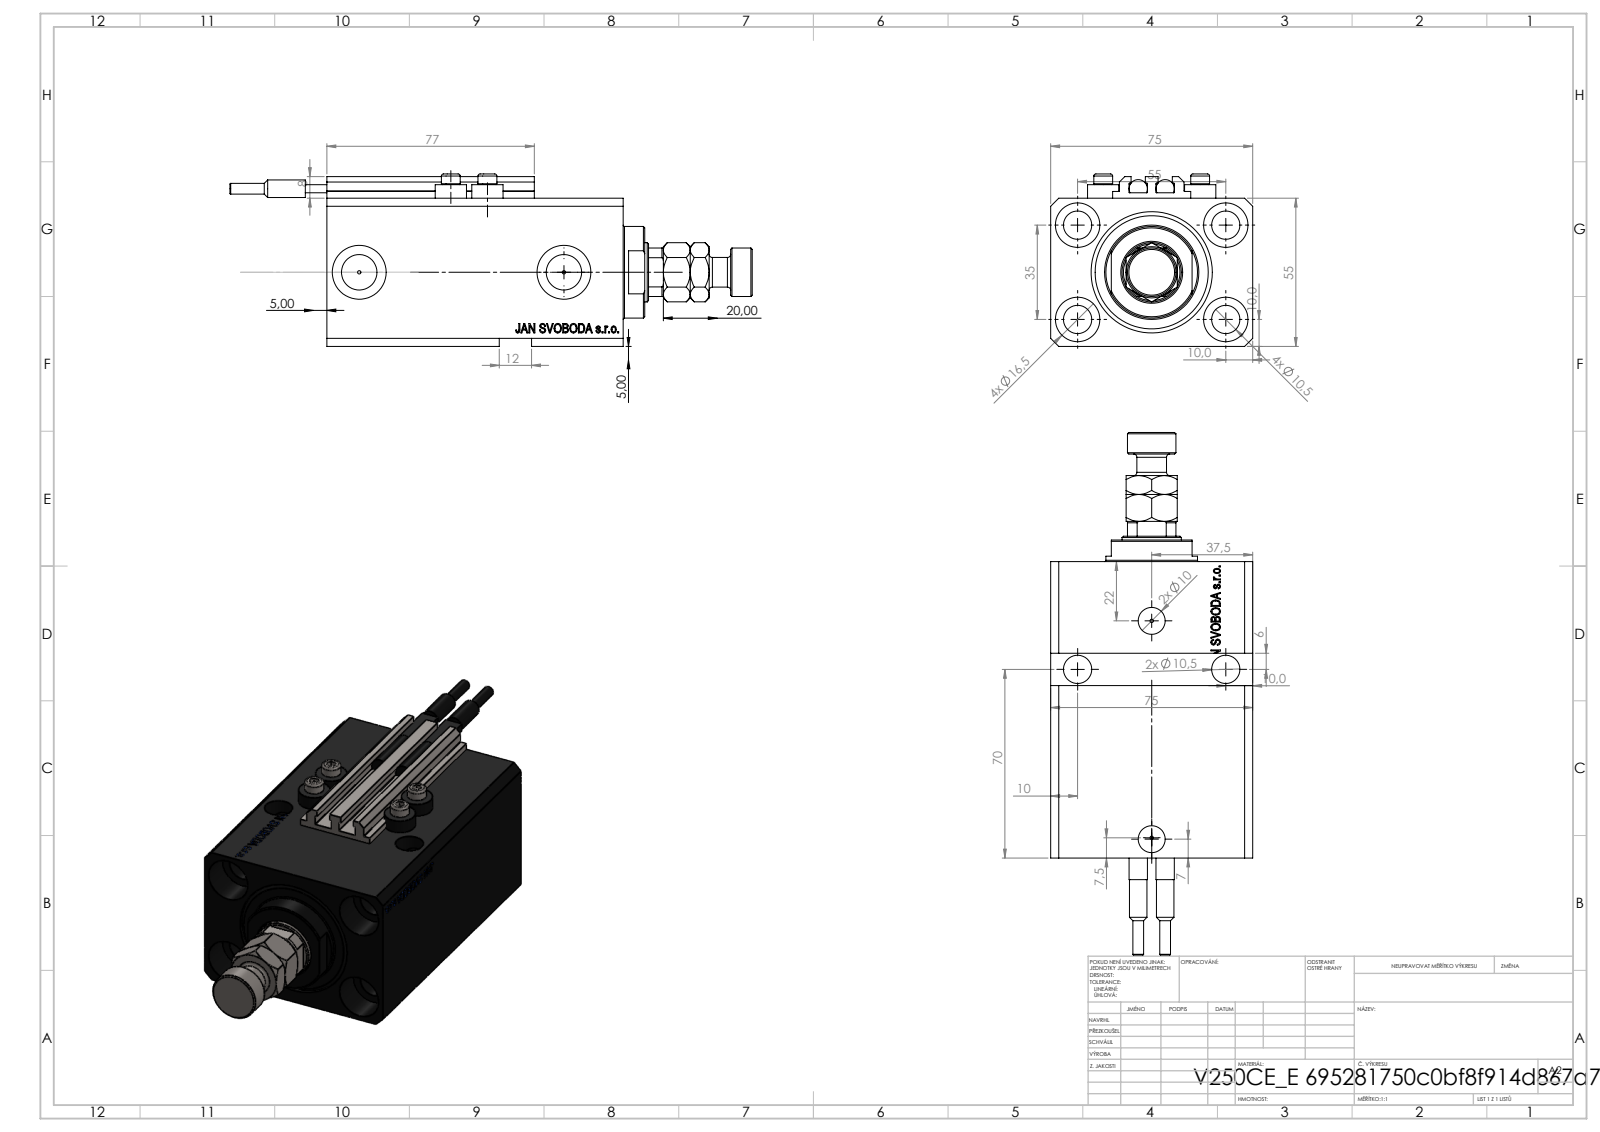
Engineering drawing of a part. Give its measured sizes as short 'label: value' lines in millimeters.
name: V250CE_C_VCP; MFA; V250CE_VC_E; V250CE_E_Body (+2 more)
written by: SolidWorks 2019 (CONFIG_CONTROL_DESIGN)
unit: mm
bodies: 11 solids, 1188 faces (562 planar, 162 cylindrical, 464 other)
size: 194 × 75 × 64
volume: 392 978 mm³; area: 101 090 mm²
holes: 9× ⌀10.5, 4× ⌀1.25, 4× ⌀4, 4× ⌀16.5, 2× ⌀10, 2× ⌀13.16, 2× ⌀20, 1× ⌀22, 1× ⌀32, 1× ⌀45
bosses: 4× ⌀11.6, 4× ⌀7, 2× ⌀6.8, 2× ⌀6.5, 2× ⌀4, 1× ⌀34, 1× ⌀18, 1× ⌀11
rounds: 10× R0.2, 1× R10.5
face distances: 55, 75, 15, 3, 110, 57, 95, 9.9, 85.1, 100.1
hole spacings: 32.6, 32.87, 55, 68.74, 13.6, 14.09, 23.05, 25.81
